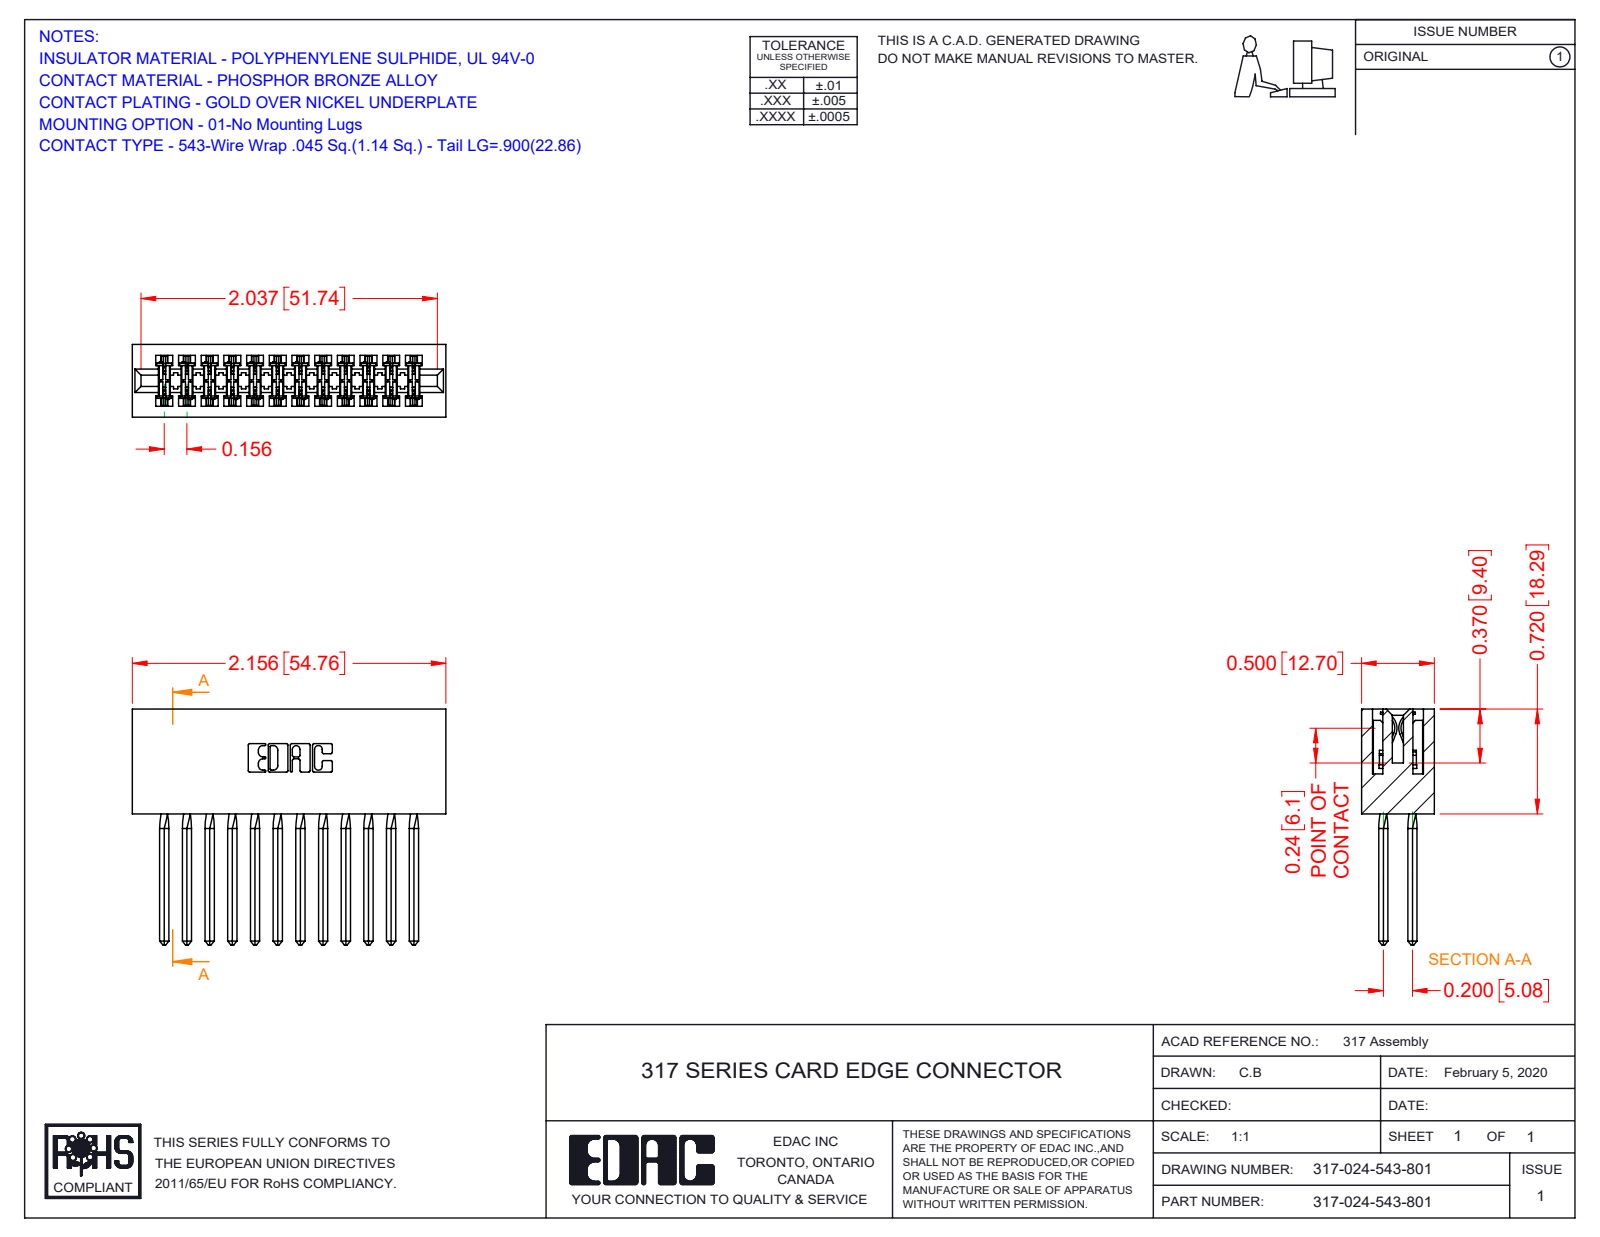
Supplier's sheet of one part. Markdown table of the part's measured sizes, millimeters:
| quantity | value |
| --- | --- |
| part name | 317-024-543-801; 317-290-001_543; 317 Part_Lugless |
| STEP written by | SolidWorks 2016 (CONFIG_CONTROL_DESIGN) |
| units | millimeters |
| bodies | 25 solids, 2226 faces (1802 planar, 328 cylindrical, 96 other) |
| overall size | 54.8 × 41.1 × 12.7 |
| volume | 10 100 mm³ |
| surface area | 14 410 mm² |
| partial cylindrical surfaces (radius × count) | 0.4 × 48, 0.3 × 22, 0.2 × 6, 0.8 × 6, 0.7 × 3, 2.4 × 2, 2.5 × 2, 2.8 × 2 |
| main face-to-face distances | 12.7, 1.9, 10.8, 2.8, 5.6, 4, 8.9, 8.4, 2.9, 15.8 |
